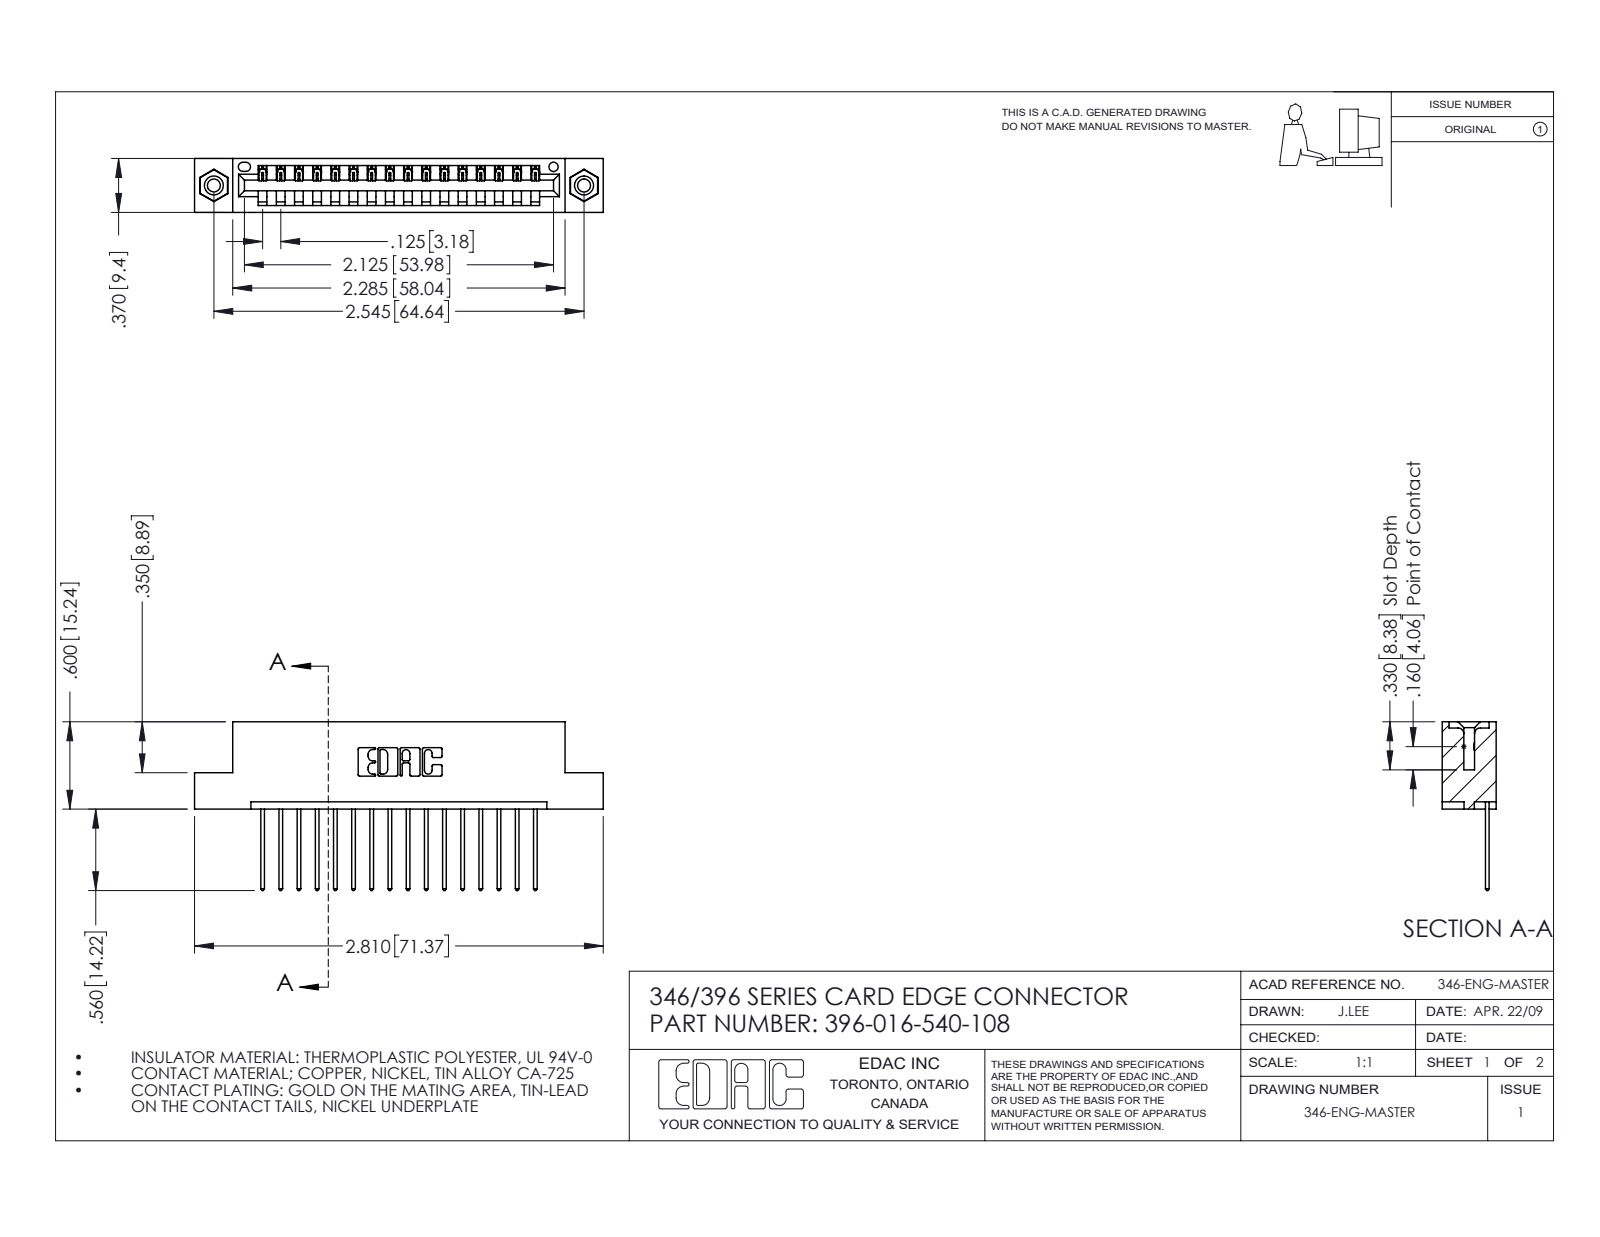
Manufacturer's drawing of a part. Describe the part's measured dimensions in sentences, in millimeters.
The part is named "345-292-001_345-293-140; 396-016-540-108; 345-250-001_345-250-003-102; 346 Part_Flush Mounting Lugs - 0.156 Dia-TI". Its 3-D file was written by "SolidWorks 2016 (CONFIG_CONTROL_DESIGN)". It is 19 solids with 1110 faces: 748 planar, 346 cylindrical and 16 other. Overall it measures 71.4 by 29.5 by 9.4 millimeters. Its volume is 6 670 cubic millimeters and its surface area 8 232 square millimeters. Round holes: 2 of diameter 2.3, 2 of diameter 3.2, 2 of diameter 4, 1 of diameter 1.6. Round bosses or shafts: 2 of diameter 3.9. Partial cylindrical surfaces (rounded edges, fillets, slot ends): 32 of radius 0.2, 32 of radius 0.3, 22 of radius 0.3, 6 of radius 0.2, 6 of radius 0.8, 3 of radius 0.7, 2 of radius 0.8, 2 of radius 1. The main face-to-face distances are 1.2, 8.2, 6.4, 9.4, 1.8, 7.6, 0.6, 3.8, 5.6, 2.5. The hole center spacings are 6.2, 59.4, 64.6.
